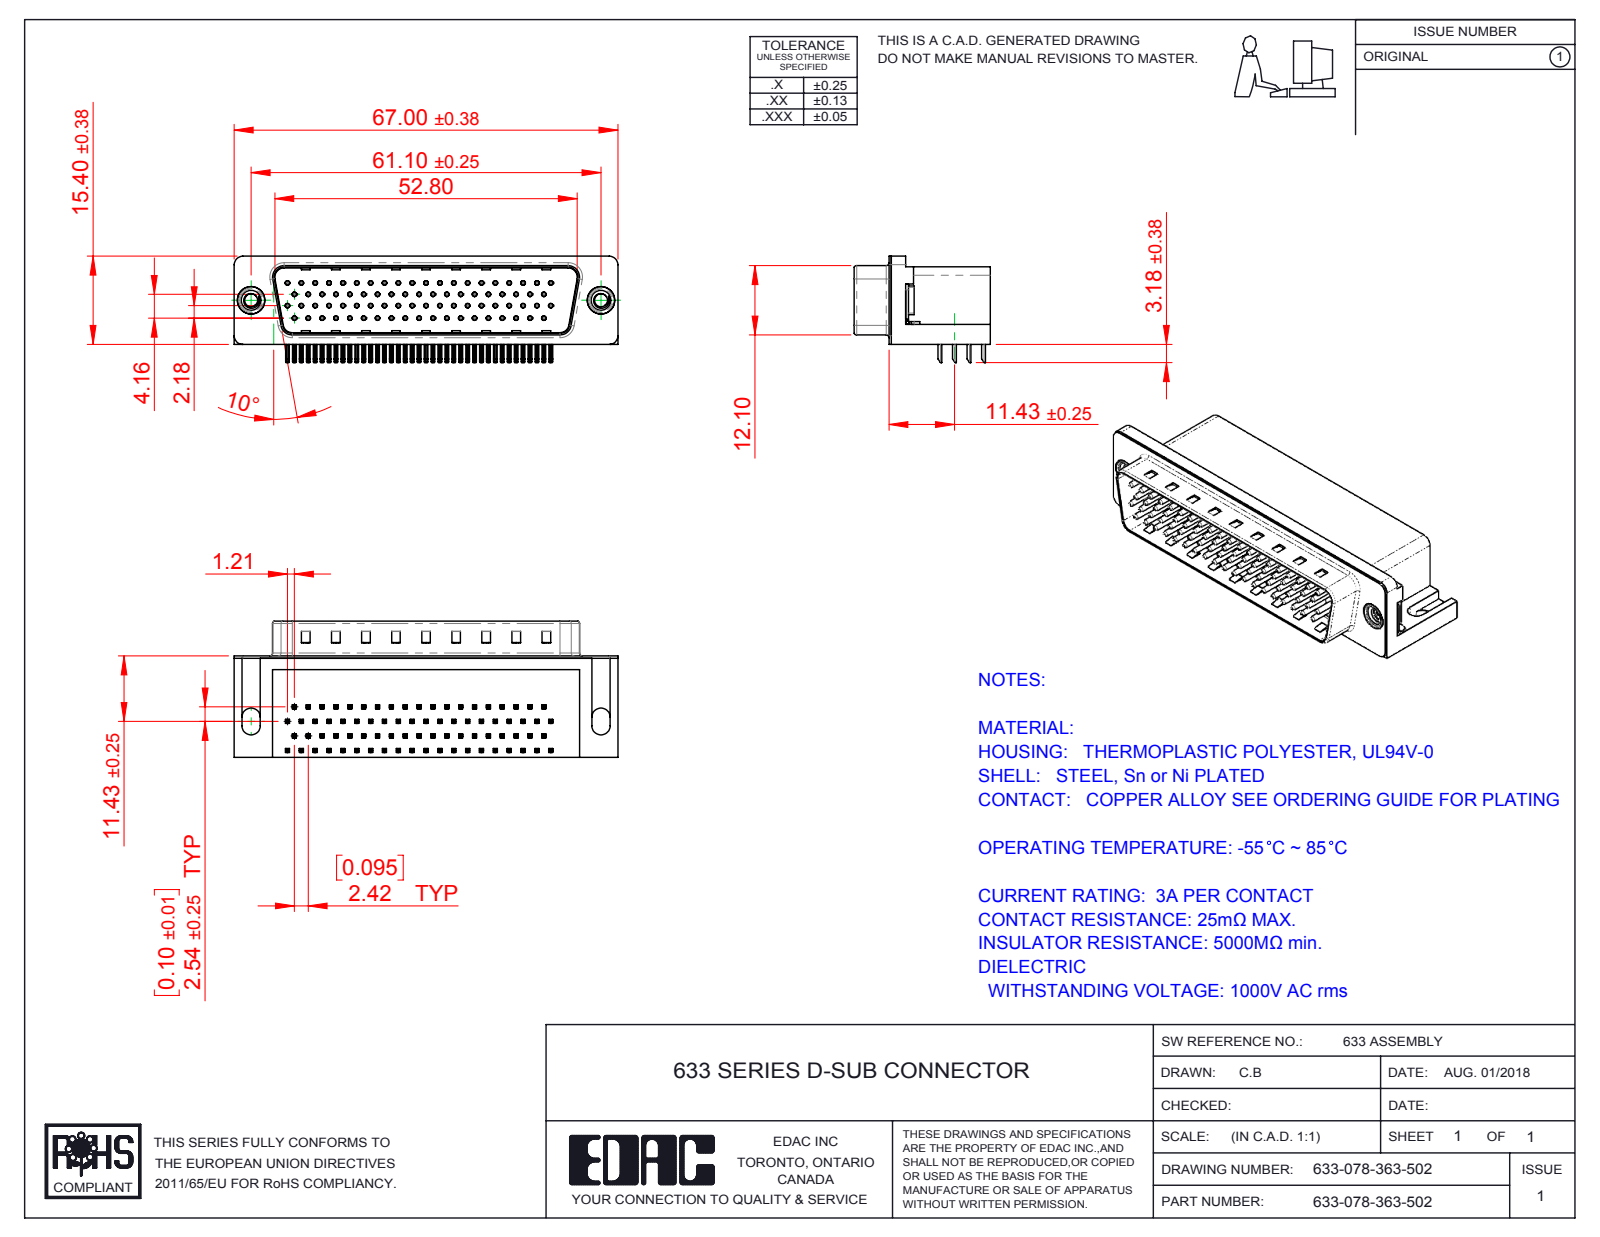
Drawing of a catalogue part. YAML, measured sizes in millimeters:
part_name: "633-078-363-502; 633 4-40 Threaded Rivet; 633 Shell_78 Contact; 633 Contact Bottom_78 Contact (+5 more)"
step_written_by: "SolidWorks 2016 (CONFIG_CONTROL_DESIGN)"
units: millimeters
bodies: {solids: 84, faces: 6270, planar: 3979, cylindrical: 1774, other: 517}
overall_size: [67, 23.8, 18.58]
volume: 14566
surface_area: 16125
round_holes:
  - {diameter: 0.35, count: 78}
  - {diameter: 0.8, count: 78}
  - {diameter: 2.26, count: 2}
  - {diameter: 4, count: 2}
  - {diameter: 4.8, count: 2}
  - {diameter: 5, count: 2}
round_bosses_or_shafts:
  - {diameter: 0.75, count: 78}
  - {diameter: 4.9, count: 2}
  - {diameter: 4.75, count: 2}
  - {diameter: 3.9, count: 2}
partial_cylinders:
  - {radius: 0.25, count: 320}
  - {radius: 0.12, count: 156}
  - {radius: 1, count: 16}
  - {radius: 0.5, count: 9}
  - {radius: 1.6, count: 8}
  - {radius: 1.5, count: 6}
  - {radius: 0.45, count: 4}
  - {radius: 0.9, count: 4}
face_to_face_distances: [0.4, 13.2, 17.3, 11.7, 13.35, 2.05, 13.75, 1.65, 11.9, 1.85]
hole_center_spacings: [2.42, 4.84, 7.26, 9.68, 6.26, 7.13, 12.1, 8.62]
